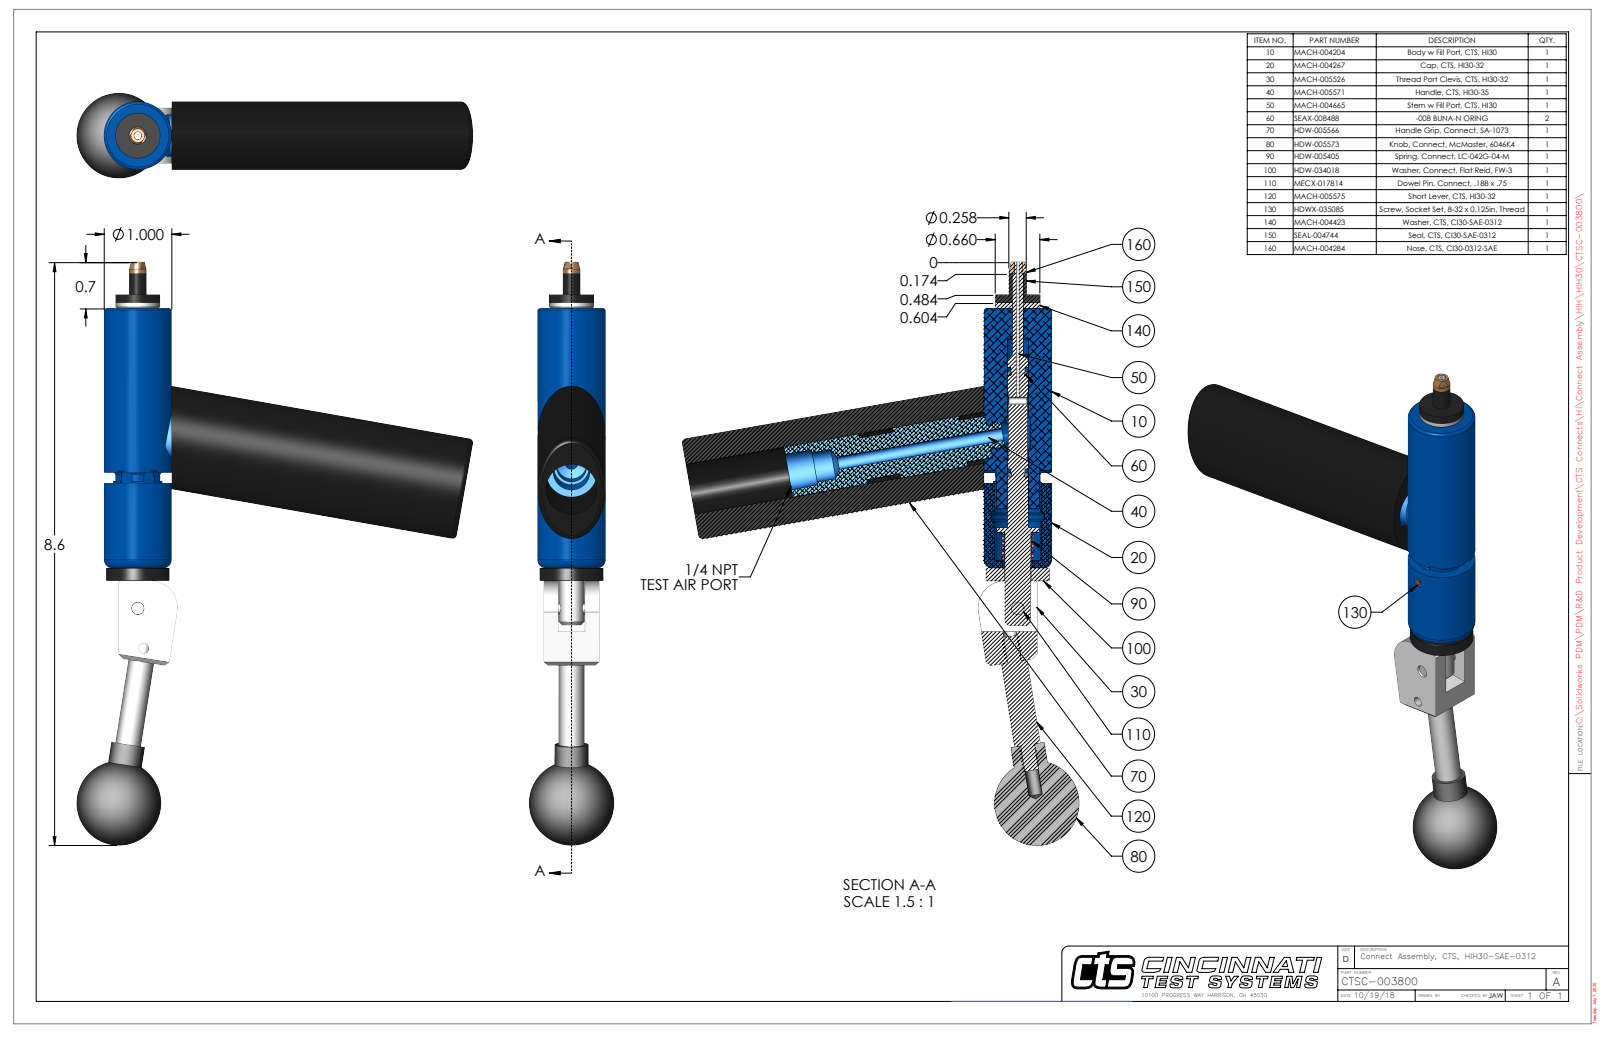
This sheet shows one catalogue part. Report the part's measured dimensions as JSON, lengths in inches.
{"part_name": "CTSC-003800", "step_written_by": "SolidWorks 2023 (AUTOMOTIVE_DESIGN)", "units": "inches", "bodies": {"solids": 11, "faces": 308, "planar": 115, "cylindrical": 126, "other": 67}, "overall_size": [8.618, 5.856, 1.25], "volume_in3": 9.24, "surface_area_in2": 74.21, "round_holes": [[0.201, 2], [0.04, 1], [0.091, 1], [0.113, 1], [0.136, 1], [0.15, 1], [0.155, 1], [0.161, 1], [0.164, 1], [0.187, 1], [0.189, 1], [0.385, 1]], "round_bosses_or_shafts": [[1, 1], [0.936, 1], [0.75, 1], [0.66, 1], [0.62, 1], [0.5, 1], [0.38, 1], [0.375, 1]], "partial_cylinders_radius": [[0.093, 6], [0.015, 1], [0.054, 1], [0.325, 1], [0.375, 1], [0.4, 1], [0.462, 1], [0.474, 1]], "face_to_face_distances": [0.21, 0.602, 3.837, 0.812, 4.024, 0.187, 0.08, 3.917, 4.104, 0.391], "hole_center_spacings": [0.599, 1.658, 2.252]}
